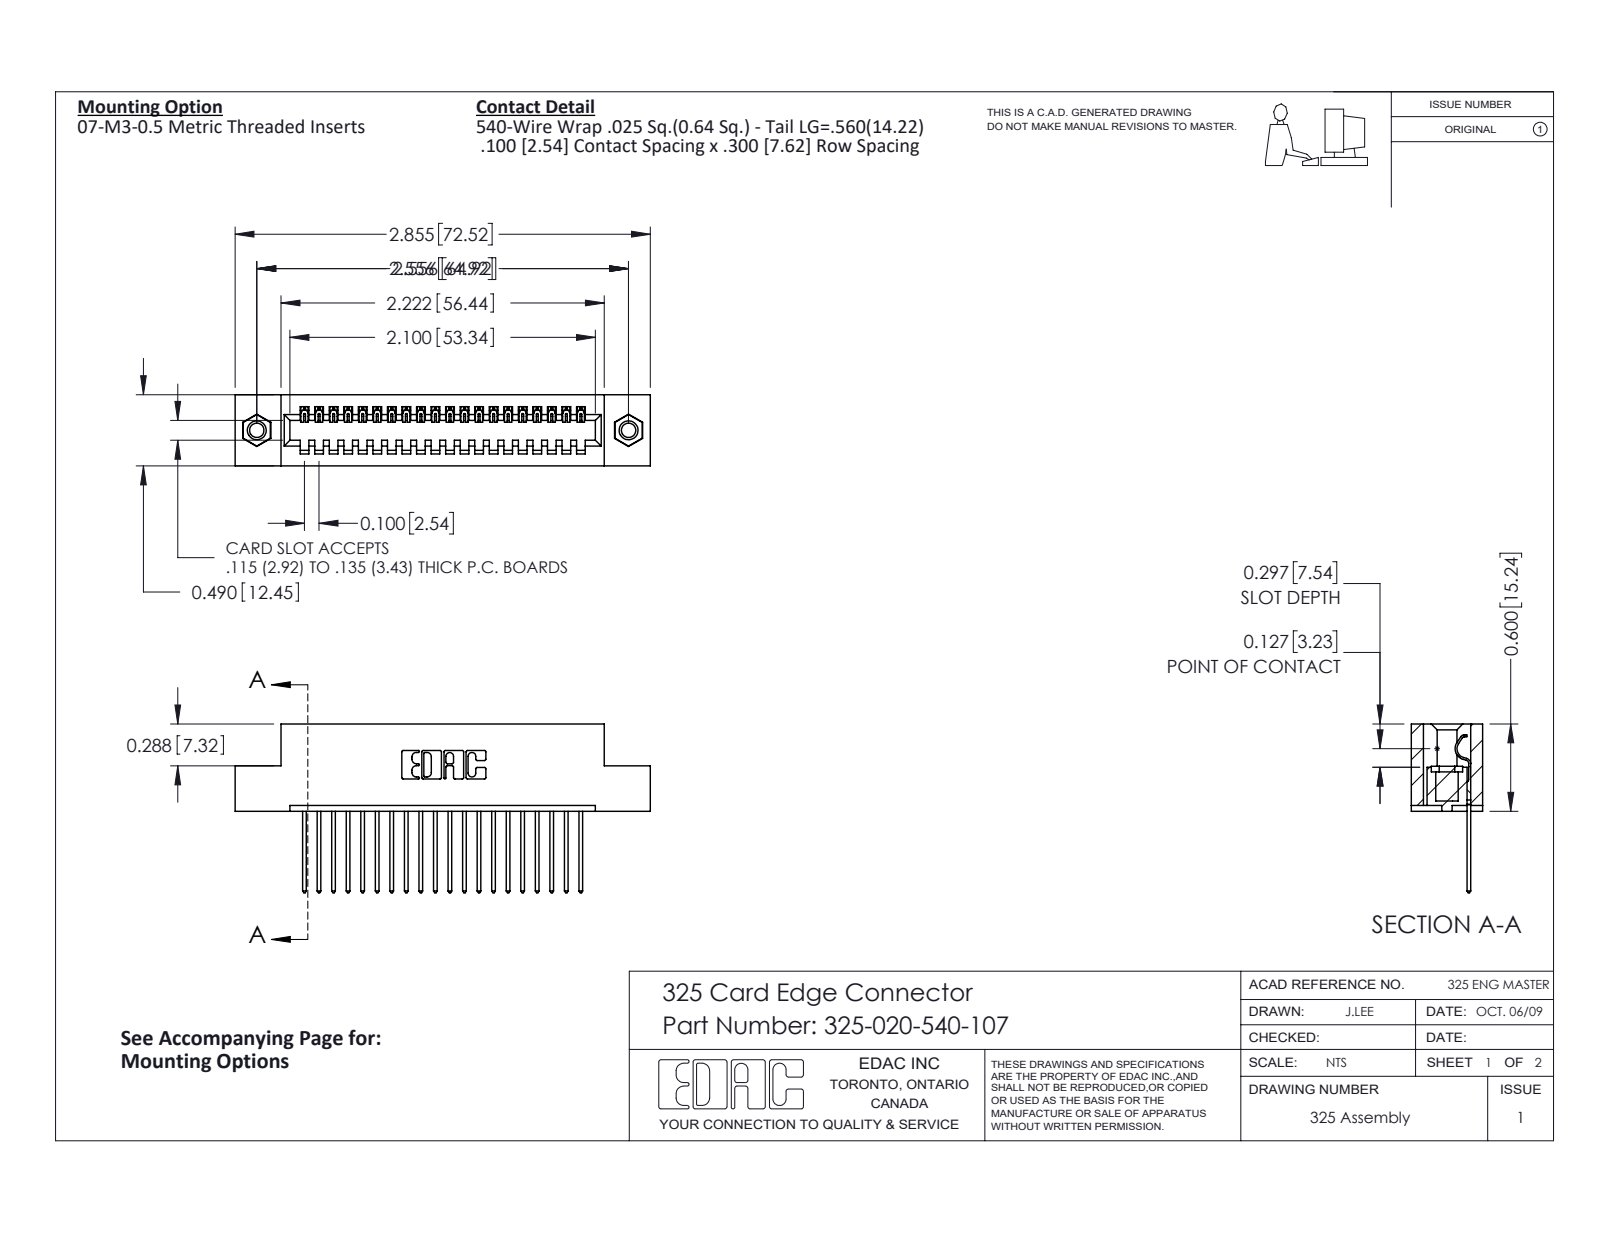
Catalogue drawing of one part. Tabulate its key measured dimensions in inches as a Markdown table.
| quantity | value |
| --- | --- |
| part name | 325 Part_TI; 325-020-540-107; 345-250-001_345-250-005-103; 325-292-001_325-293-140 |
| STEP written by | SolidWorks 2016 (CONFIG_CONTROL_DESIGN) |
| units | inches |
| bodies | 23 solids, 1334 faces (942 planar, 376 cylindrical, 16 other) |
| overall size | 2.855 × 1.16 × 0.49 |
| volume | 0.552 in³ |
| surface area | 15.09 in² |
| round holes (diameter × count) | 0.098 × 2, 0.125 × 2, 0.16 × 2 |
| round bosses / shafts (diameter × count) | 0.155 × 2 |
| partial cylindrical surfaces (radius × count) | 0.006 × 40, 0.01 × 40, 0.01 × 22, 0.007 × 6, 0.031 × 6, 0.026 × 3, 0.014 × 1, 0.022 × 1 |
| main face-to-face distances | 0.083, 0.407, 0.3, 0.49, 0.107, 0.383, 0.025, 0.04, 0.1, 0.325 |
| hole center spacings | 2.556 |
